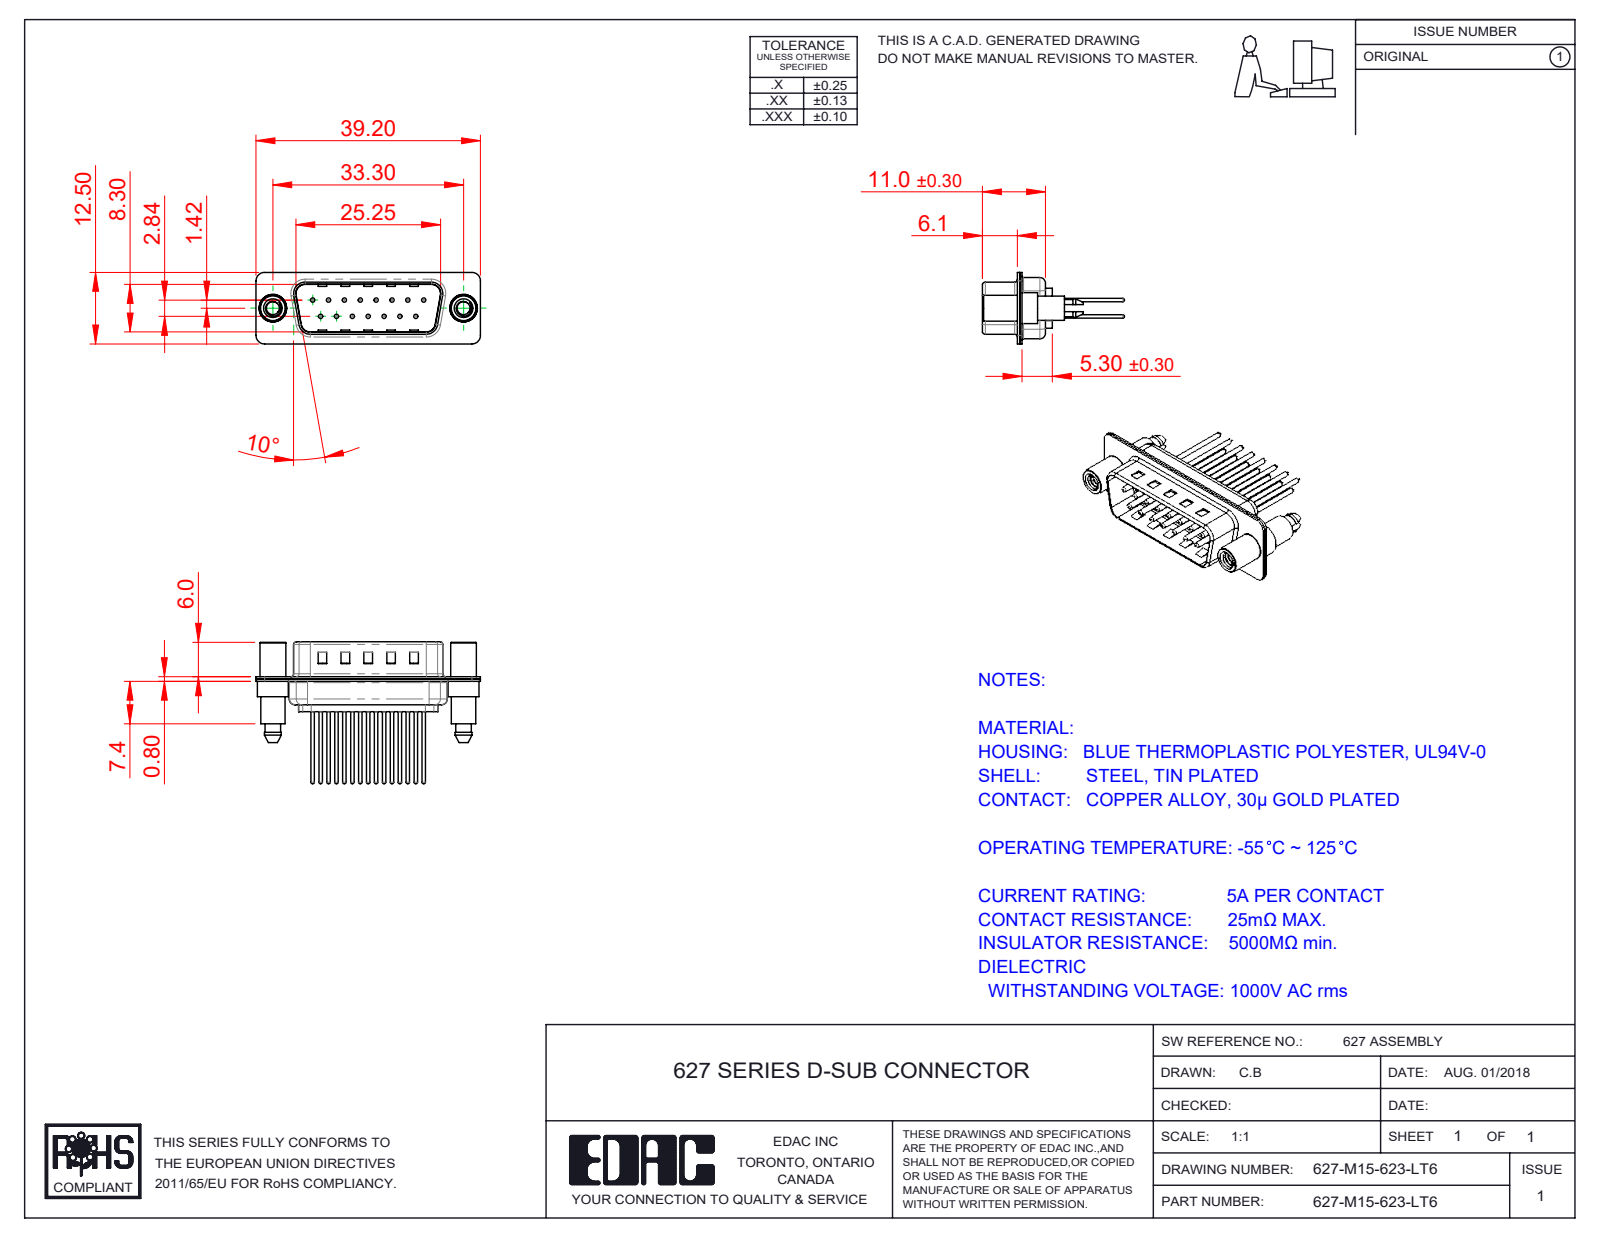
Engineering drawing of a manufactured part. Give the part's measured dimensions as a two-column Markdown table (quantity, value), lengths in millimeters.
| quantity | value |
| --- | --- |
| part name | 627-M15-623-LT6; 627M Contact Row 1_23; 627M Contact Row 2_23; 627M Housing_15 Contacts (+3 more) |
| STEP written by | SolidWorks 2020 (CONFIG_CONTROL_DESIGN) |
| units | millimeters |
| bodies | 20 solids, 947 faces (262 planar, 371 cylindrical, 314 other) |
| overall size | 39.2 × 24.77 × 12.5 |
| volume | 2 211 mm³ |
| surface area | 5 471 mm² |
| round holes (diameter × count) | 0.75 × 15, 1.6 × 15, 2 × 15, 2.26 × 2, 4 × 2, 4.8 × 2 |
| round bosses / shafts (diameter × count) | 1.5 × 15, 0.6 × 15, 5.4 × 2, 4.9 × 2, 4.5 × 2, 4.25 × 2 |
| partial cylindrical surfaces (radius × count) | 1.5 × 18, 2 × 12, 1.6 × 10, 0.5 × 8, 0.25 × 4, 0.6 × 4, 0.65 × 4, 0.9 × 4 |
| main face-to-face distances | 0.4, 0.8, 9.5, 9.1, 8.7, 9.9, 5.3, 1.2, 6.1, 5.7 |
| hole center spacings | 3.16, 2.77, 5.54, 8.31, 11.08, 5.03, 5.04, 7.48 |
